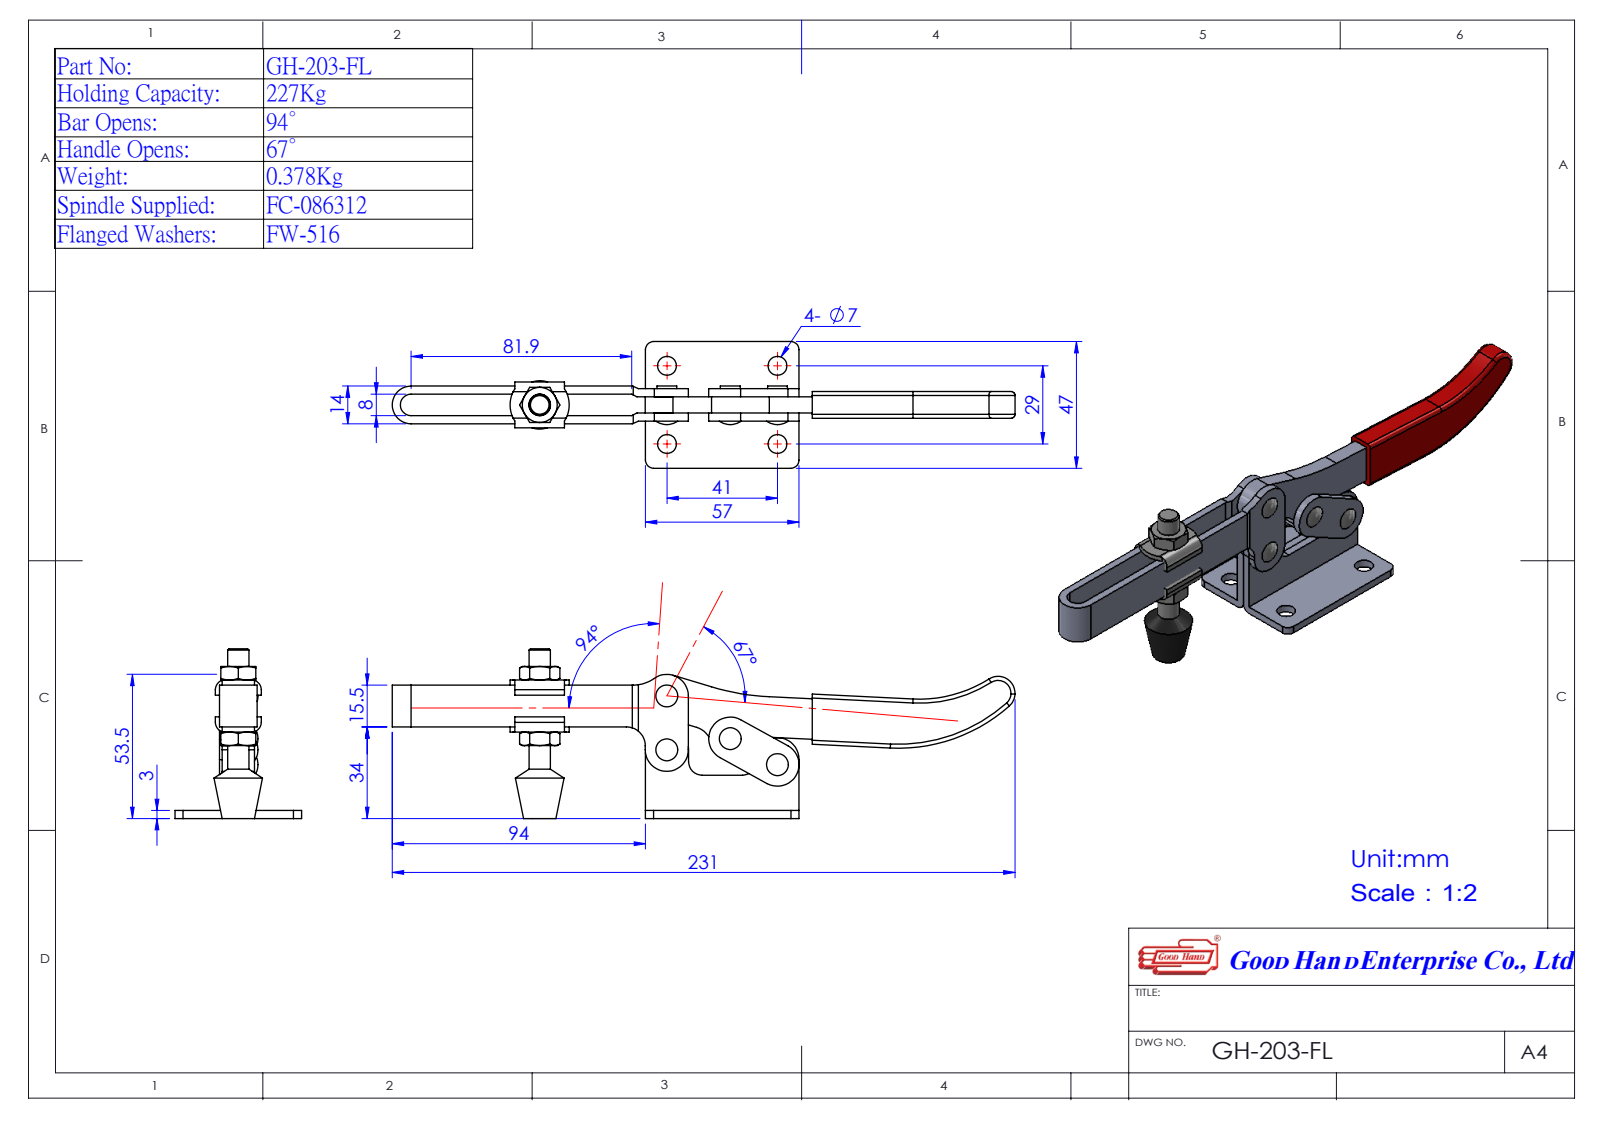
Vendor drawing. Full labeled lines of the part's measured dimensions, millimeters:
Part name (STEP PRODUCT): Group2^GH-203-FL(簡化)-1; Group5^GH-203-FL(簡化)-1; Group4^GH-203-FL(簡化)-1; Group1^GH-203-FL(簡化) (+2 more)
STEP written by: SolidWorks 2016 (AUTOMOTIVE_DESIGN)
Units: millimetres
Bodies: 5 solids, 242 faces (107 planar, 97 cylindrical, 38 other)
Overall size (bounding box): 231.21 × 63 × 47
Volume: 57 313 mm³ · Surface area: 33 274 mm²
Round holes (diameter × count): ⌀5 ×4, ⌀7 ×4, ⌀6.33 ×1
Round bosses / shafts (diameter × count): ⌀7.35 ×4, ⌀16 ×1, ⌀7.93 ×1
Partial cylindrical surfaces — rounded edges, fillets, slot ends (radius × count): R8 ×6, R1.2 ×4, R3 ×4, R3.6 ×4, R5 ×2, R7 ×2, R11.04 ×2, R4 ×1
Main face-to-face distances: 1, 2, 3, 10, 9, 11, 8, 12, 6, 4
Hole centre spacings: 20, 29, 41, 50.22, 23.84, 28.4, 41.37, 48.35
